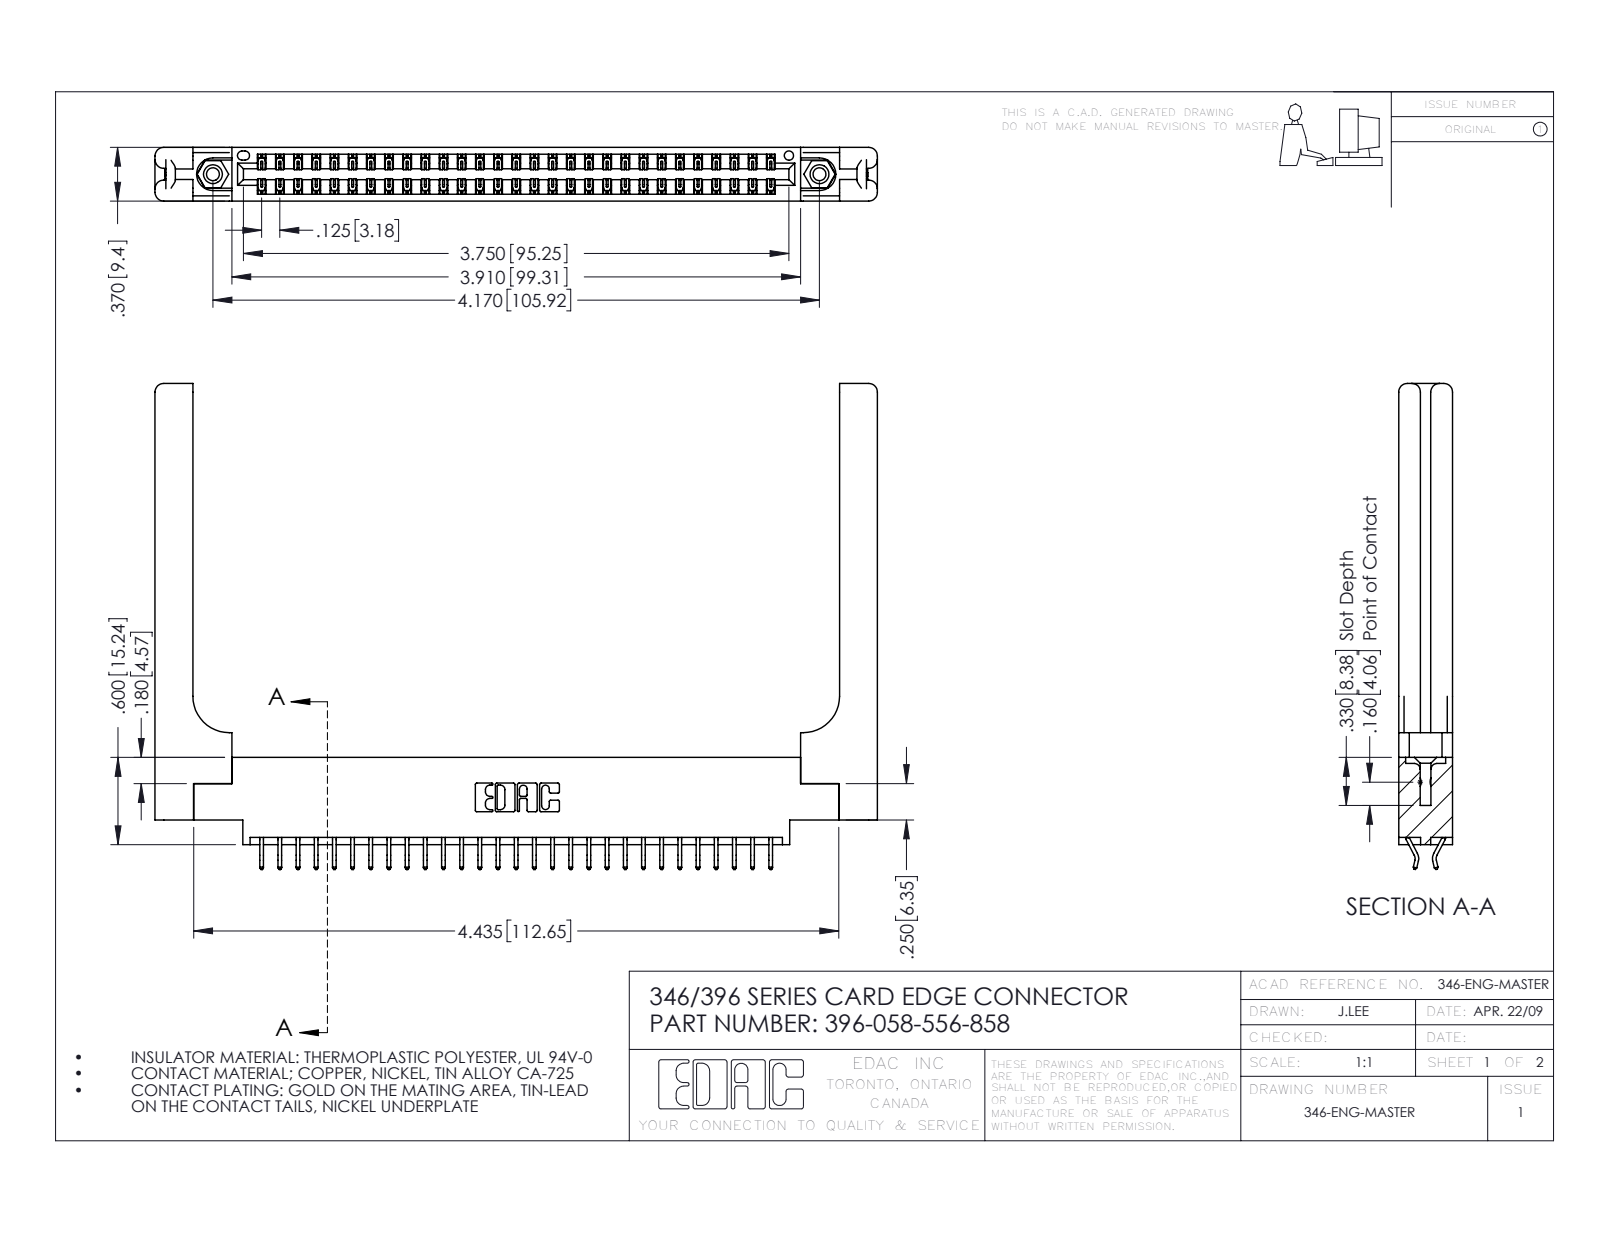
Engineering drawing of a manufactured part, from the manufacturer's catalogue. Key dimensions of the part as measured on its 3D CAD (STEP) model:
Part name (STEP PRODUCT): 345-292-001_556 Tail; 346 Part_0.170 Offset - 0.156 Dia-TH; 346-220-058_345-220-058; 345-250-001_345-250-001-102 (+1 more)
STEP written by: SolidWorks 2016 (CONFIG_CONTROL_DESIGN)
Units: inches
Bodies: 63 solids, 3746 faces (2490 planar, 1196 cylindrical, 60 other)
Overall size (bounding box): 4.966 × 3.34 × 0.37
Volume: 1.192 in³ · Surface area: 33.24 in²
Round holes (diameter × count): ⌀0.089 ×2, ⌀0.125 ×2, ⌀0.156 ×2, ⌀0.064 ×1
Round bosses / shafts (diameter × count): ⌀0.155 ×2
Partial cylindrical surfaces — rounded edges, fillets, slot ends (radius × count): R0.006 ×87, R0.01 ×22, R0.06 ×16, R0.007 ×6, R0.031 ×6, R0.026 ×3, R0.01 ×2, R0.014 ×2
Main face-to-face distances: 0.37, 0.048, 0.322, 0.072, 0.15, 0.148, 0.25, 0.025, 0.298, 0.275
Hole centre spacings: 0.246, 3.962, 4.17
